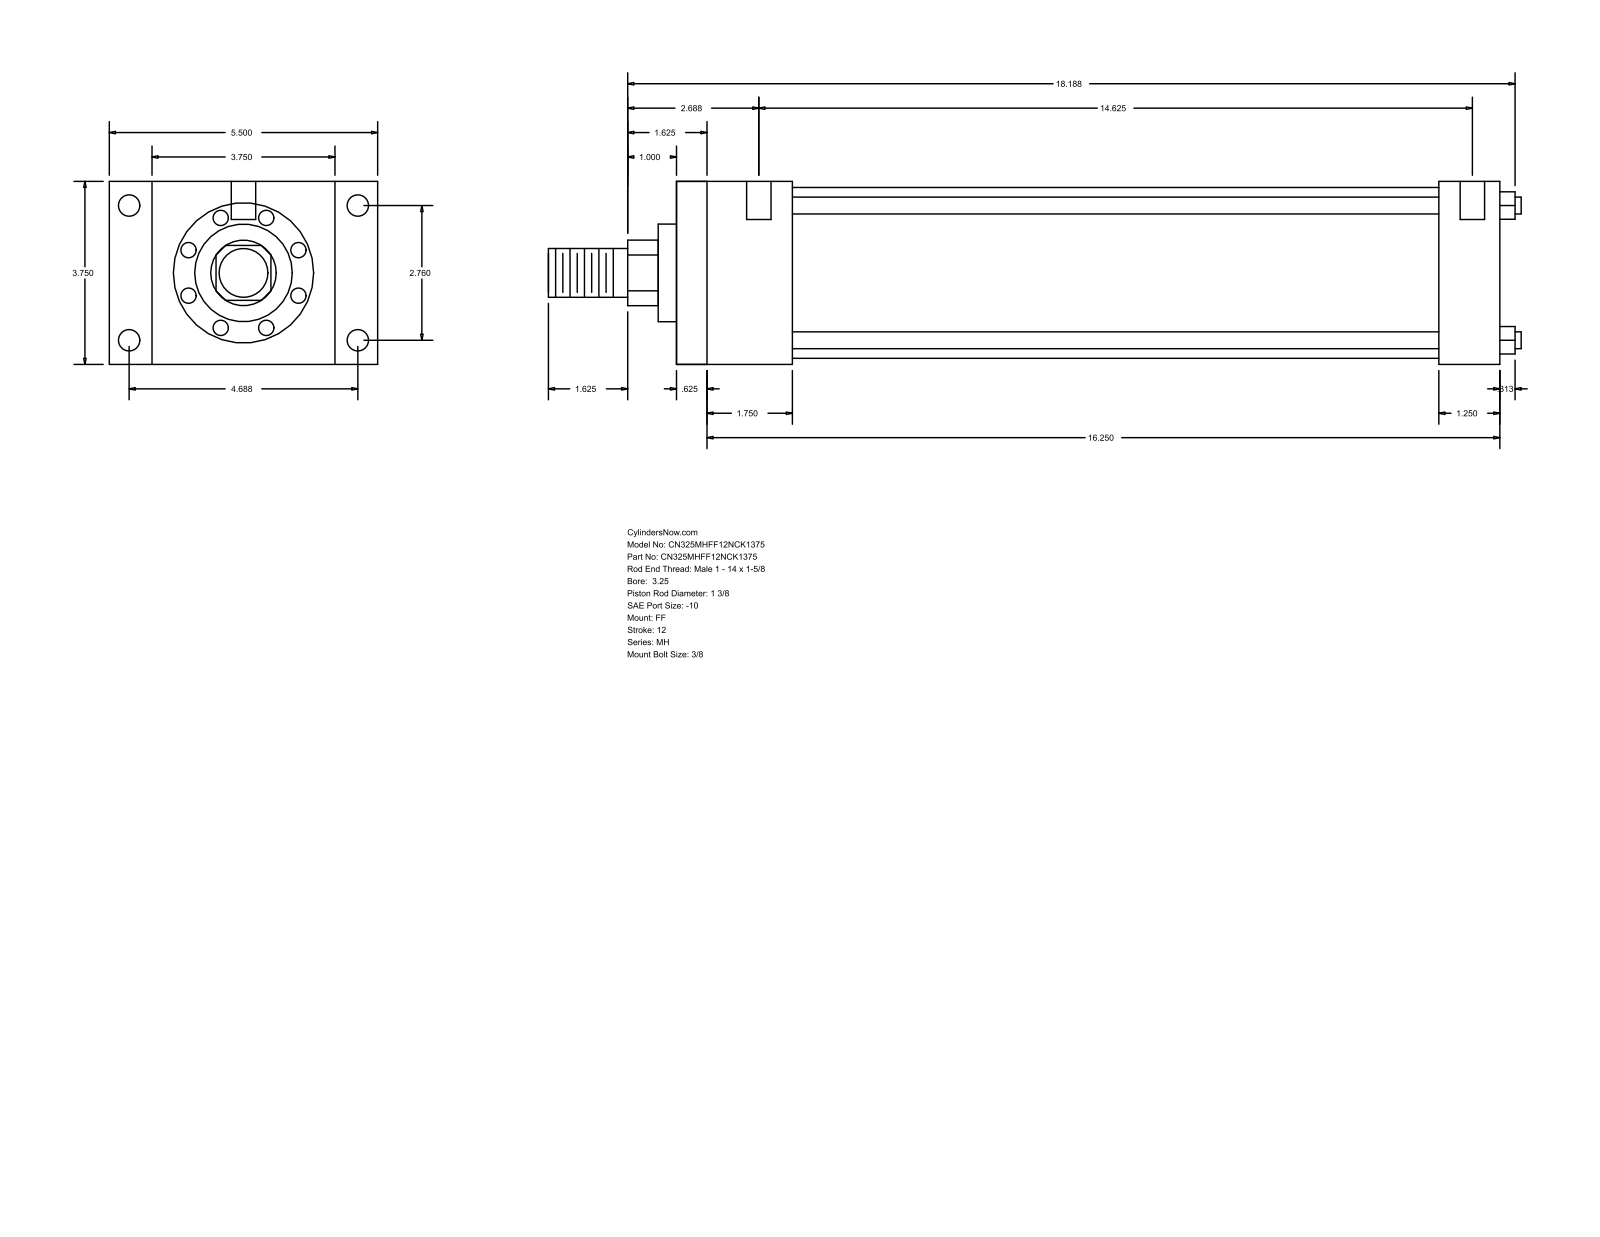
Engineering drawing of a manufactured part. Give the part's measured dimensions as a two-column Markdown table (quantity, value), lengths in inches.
| quantity | value |
| --- | --- |
| part name | MH_FF__0325_1.375 |
| STEP written by | GSSL Pune (CONFIG_CONTROL_DESIGN) |
| units | inches |
| bodies | 0 solids, 92 faces (64 planar, 28 cylindrical, 0 other) |
| overall size | 19.937 × 5.5 × 3.75 |
| round holes (diameter × count) | 0.219 × 4, 0.438 × 4, 0.5 × 2 |
| round bosses / shafts (diameter × count) | 0.345 × 4, 3.5 × 1, 2 × 1, 1.375 × 1, 1 × 1 |
| partial cylindrical surfaces (radius × count) | 0.672 × 1 |
| main face-to-face distances | 3.75, 16.875, 0.625, 16.25, 0.875, 4.625, 15.625, 15, 1.25, 2.375 |
| hole center spacings | 2.76, 4.687, 5.439, 14.875, 0.063, 0.187, 14.625, 14.688 |
